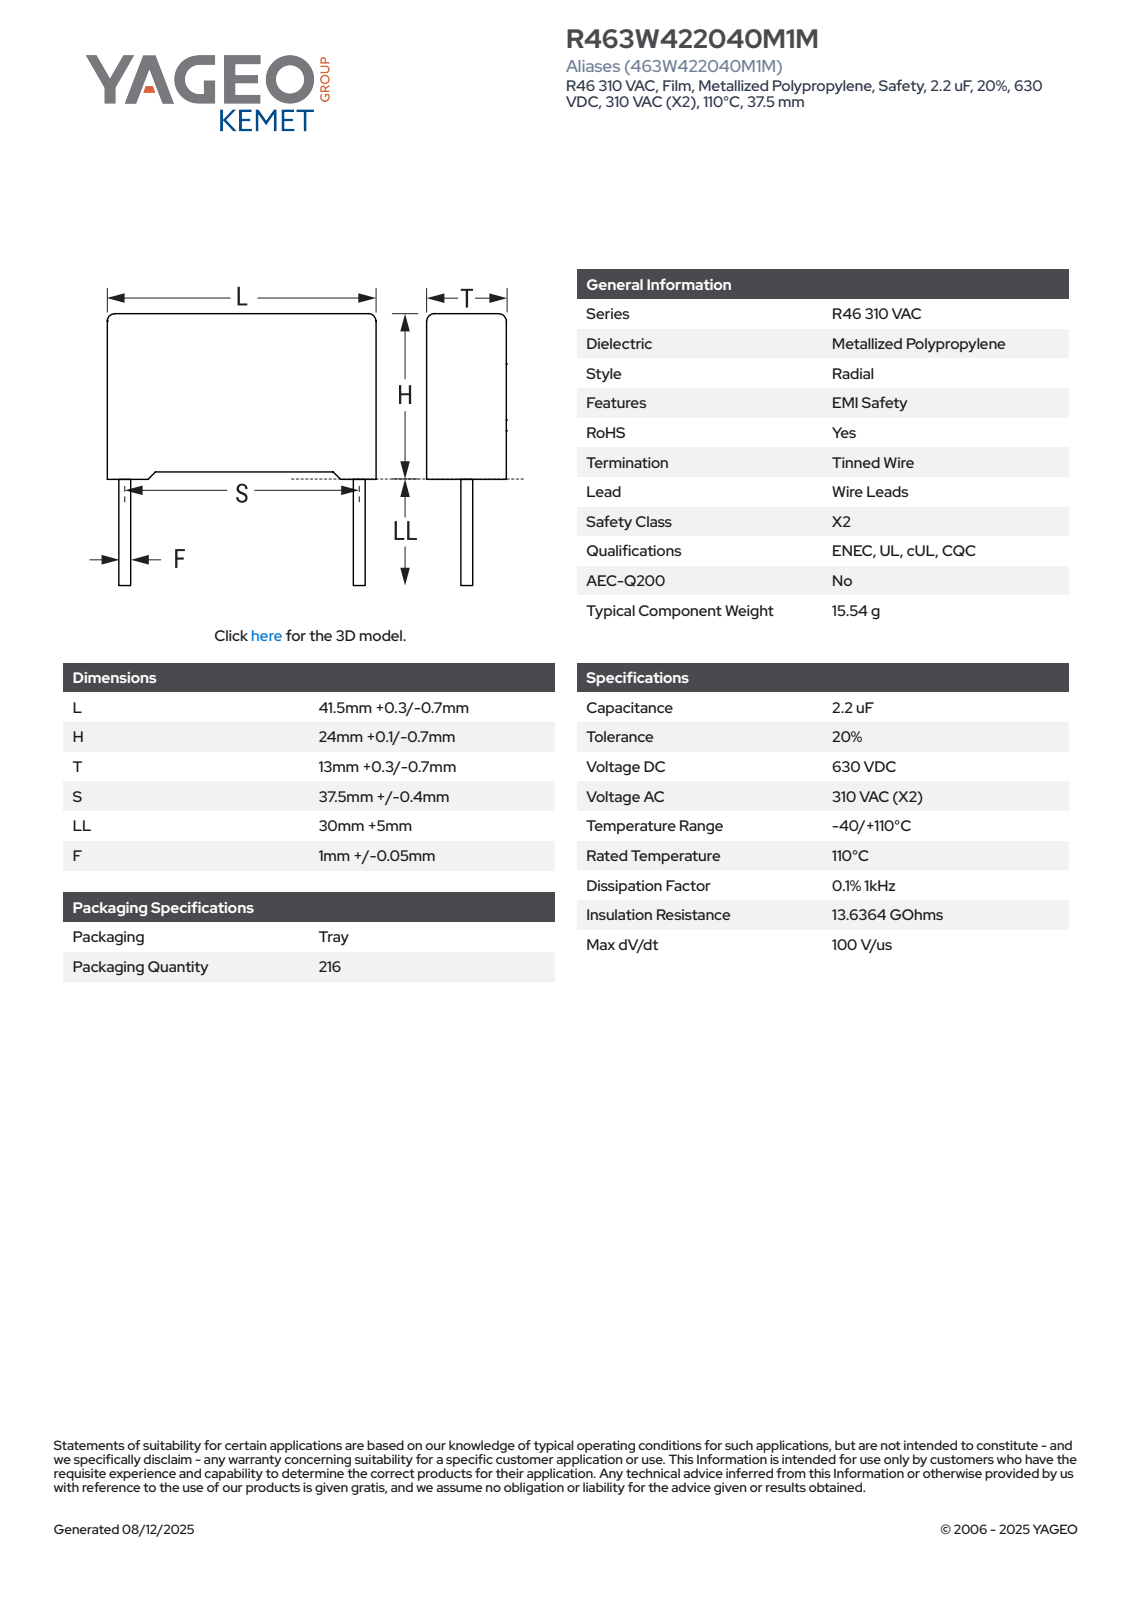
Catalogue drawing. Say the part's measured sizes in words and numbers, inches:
The part is named "CFR_RB2_41.5X24X13_L41.8H24.1T13.3S37.5LL35F1.05". Its 3-D file was written by "SolidWorks 2021 (AUTOMOTIVE_DESIGN)". It is 4 solids with 85 faces: 77 planar, 8 cylindrical and 0 other. Overall it measures 2.327 by 1.646 by 0.524 inches. Its volume is 0.796 cubic inches and its surface area 6.326 square inches. Round bosses or shafts: 2 of diameter 0.041. Partial cylindrical surfaces (rounded edges, fillets, slot ends): 4 of radius 0.02. The main face-to-face distances are 0.524, 0.916, 1.646, 0.919, 0.03, 0.033, 0.949, 0.524, 0.055, 1.591.
